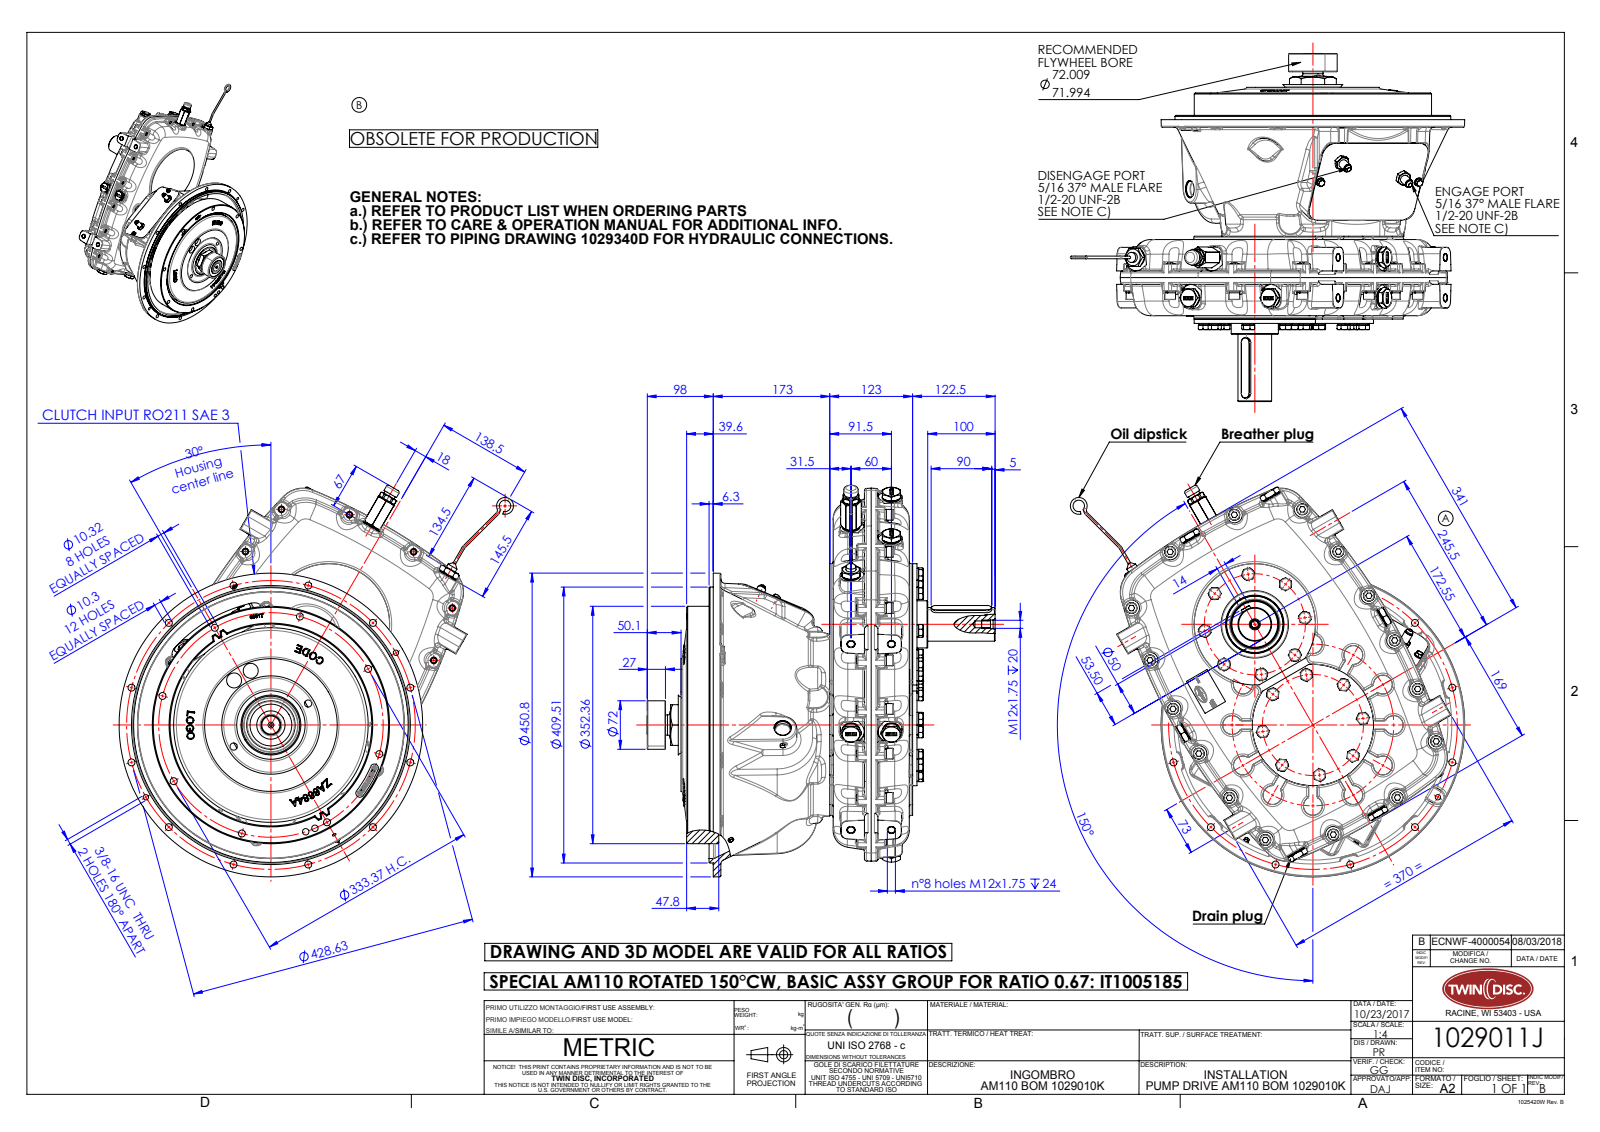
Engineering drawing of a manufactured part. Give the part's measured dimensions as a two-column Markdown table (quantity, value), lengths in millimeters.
| quantity | value |
| --- | --- |
| part name | ITam110-013_rev01-installation; IT1048010_rev01-installation; IT4588002_rev00-installation; ITam110-019-installation (+5 more) |
| STEP written by | SolidWorks 2015 (AUTOMOTIVE_DESIGN) |
| units | millimeters |
| bodies | 62 solids, 7620 faces (2206 planar, 1500 cylindrical, 3914 other) |
| overall size | 585.62 × 581.42 × 516.6 |
| volume | 8 185 000 mm³ |
| surface area | 2 331 000 mm² |
| round holes (diameter × count) | 10.2 × 54, 8.5 × 39, 11 × 32, 12 × 21, 10.3 × 12, 18.63 × 12, 21 × 11, 13 × 9, 10.32 × 8, 10 × 7, 30 × 7, 6 × 5 |
| round bosses / shafts (diameter × count) | 10 × 32, 18.1 × 16, 16.2 × 16, 16.1 × 16, 16 × 16, 27 × 11, 25.95 × 10, 12.7 × 8 |
| partial cylindrical surfaces (radius × count) | 0.1 × 225, 3 × 164, 0.25 × 46, 24.86 × 46, 6.5 × 41, 10 × 30, 1.5 × 27, 12 × 24 |
| main face-to-face distances | 5, 118, 123, 11.5, 109.5, 113, 6.5, 124.5, 129.5, 8.5 |
| hole center spacings | 60, 120, 207.84, 231.82, 51.37, 123.96, 157.11, 62.12 |
